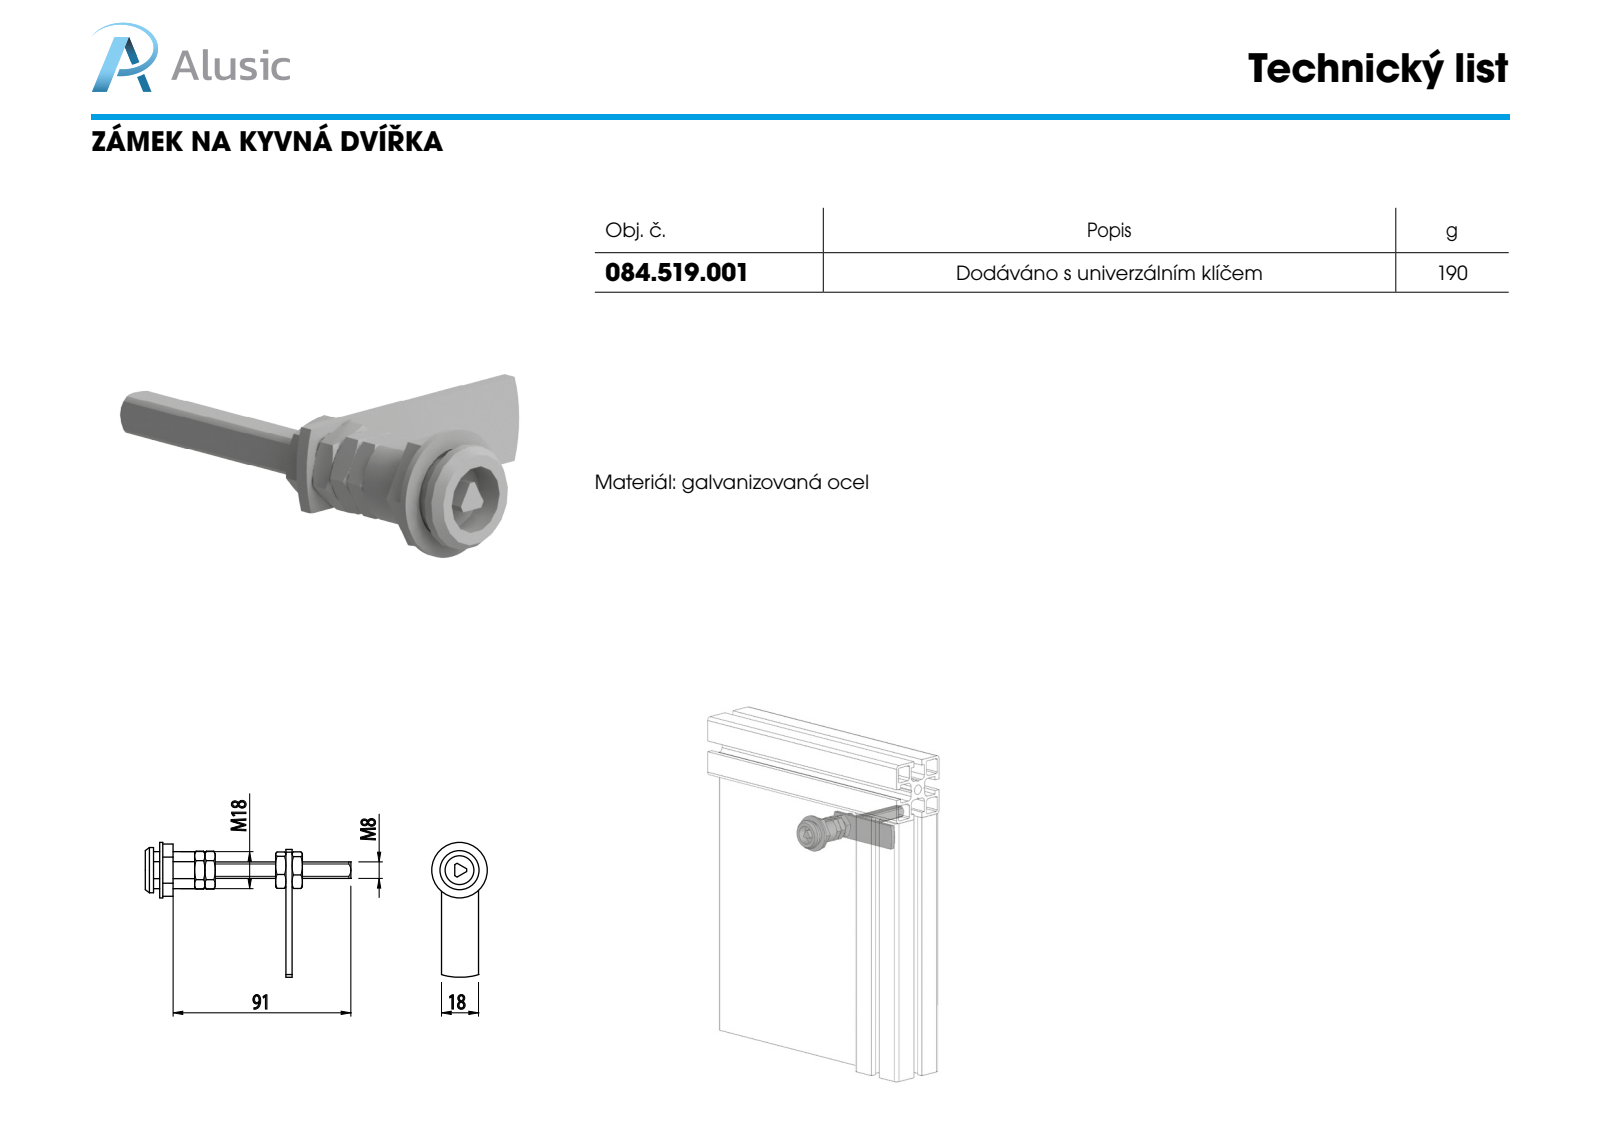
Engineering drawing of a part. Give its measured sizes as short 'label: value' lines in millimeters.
name: 084.519.001-1; 084.519.001; 084.519.001B; Hex Nut Style 1 GradeAB_ALUSIC_Hexagon Nut ISO - 4032 - M10 - D - S (+2 more)
written by: SolidWorks 2011 (CONFIG_CONTROL_DESIGN)
unit: mm
bodies: 6 solids, 177 faces (55 planar, 44 cylindrical, 78 other)
size: 60.94 × 44 × 25.4
volume: 13 538 mm³; area: 9 451 mm²
holes: 1× ⌀8.5, 1× ⌀10, 1× ⌀14, 1× ⌀16.5
bosses: 1× ⌀22
rounds: 1× R3.5, 1× R9, 1× R28.93
face distances: 3, 5, 19, 8, 15, 9.44, 16.8, 7.36, 22, 4
